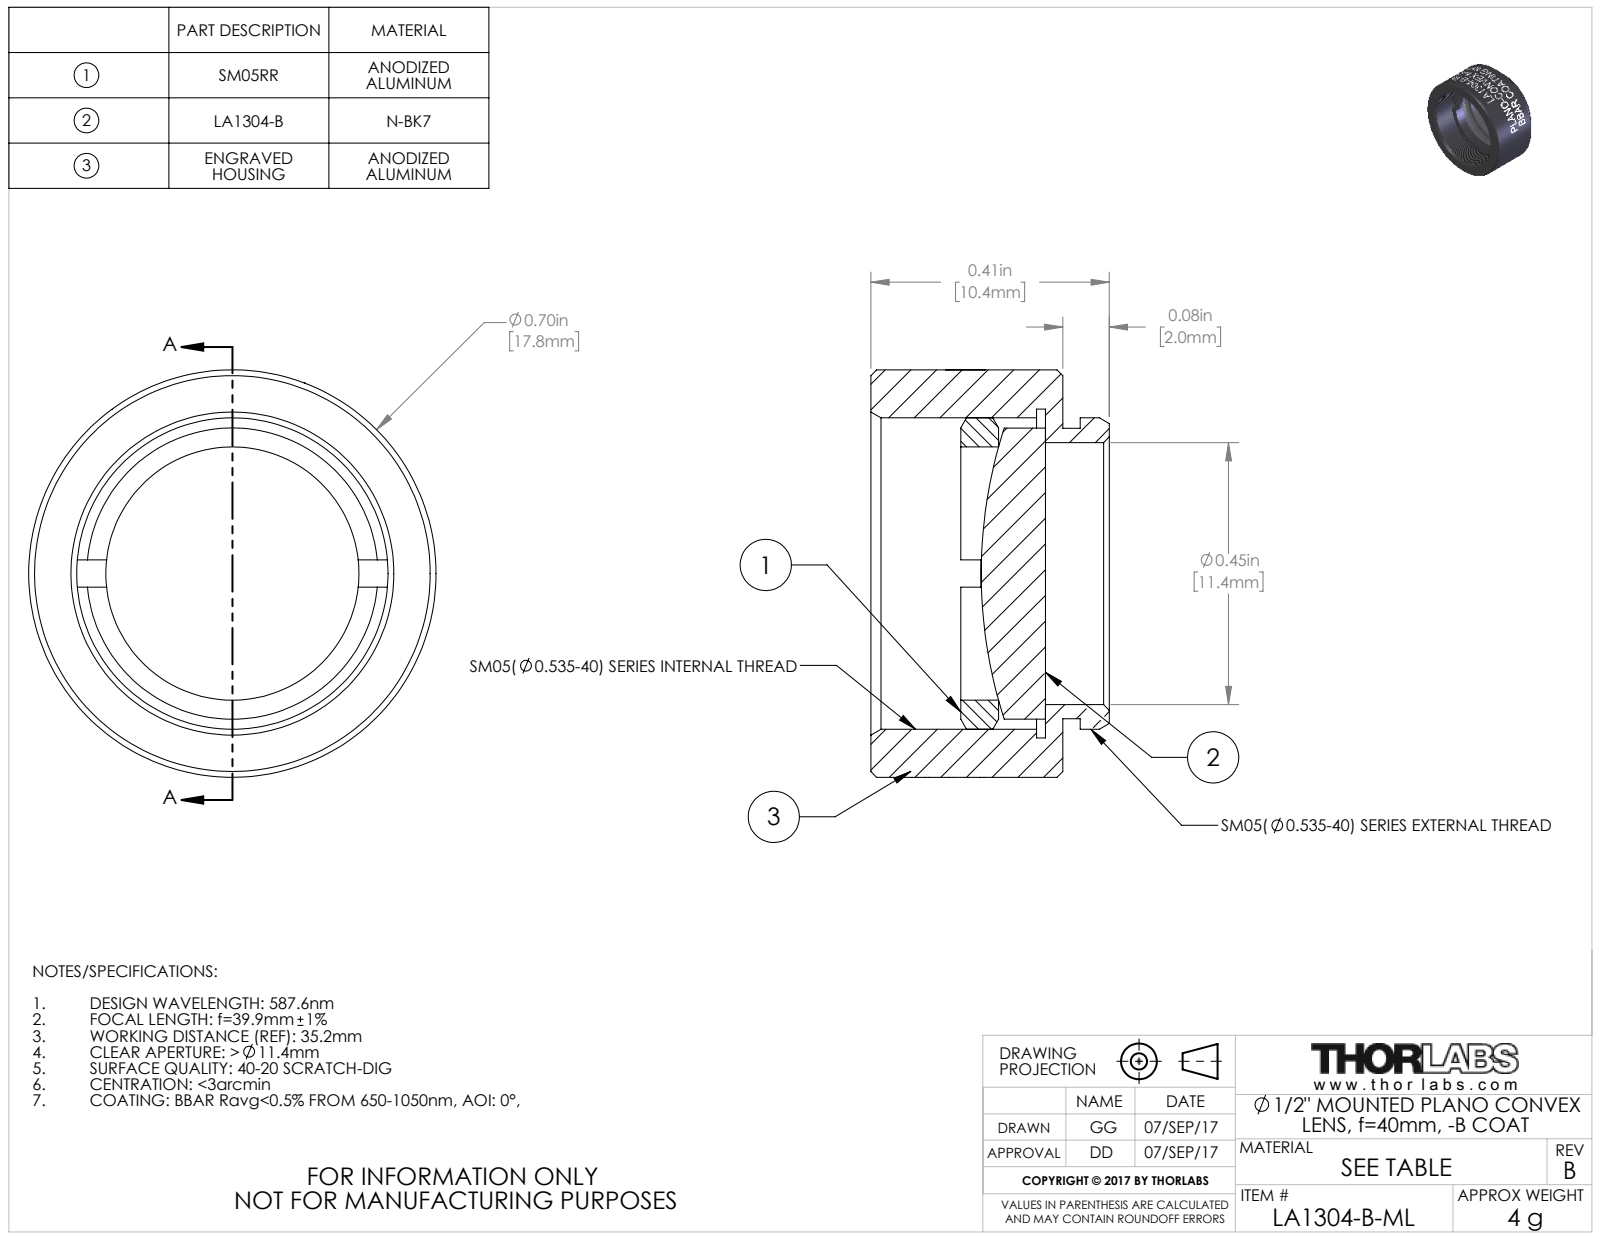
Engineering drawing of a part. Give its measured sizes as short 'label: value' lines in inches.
name: 24408-E0W
written by: SolidWorks 2016 (CONFIG_CONTROL_DESIGN)
unit: in
bodies: 3 solids, 280 faces (94 planar, 111 cylindrical, 75 other)
size: 0.7 × 0.7 × 0.41
volume: 0.081 in³; area: 2.856 in²
holes: 1× ⌀0.435, 1× ⌀0.45, 1× ⌀0.535, 1× ⌀0.565
bosses: 1× ⌀0.7, 1× ⌀0.535, 1× ⌀0.5, 1× ⌀0.499
rounds: 1× R0.35
face distances: 0.03, 0.3, 0.33, 0.22, 0.111, 0.08, 0.176, 0.145, 0.065, 0.155
